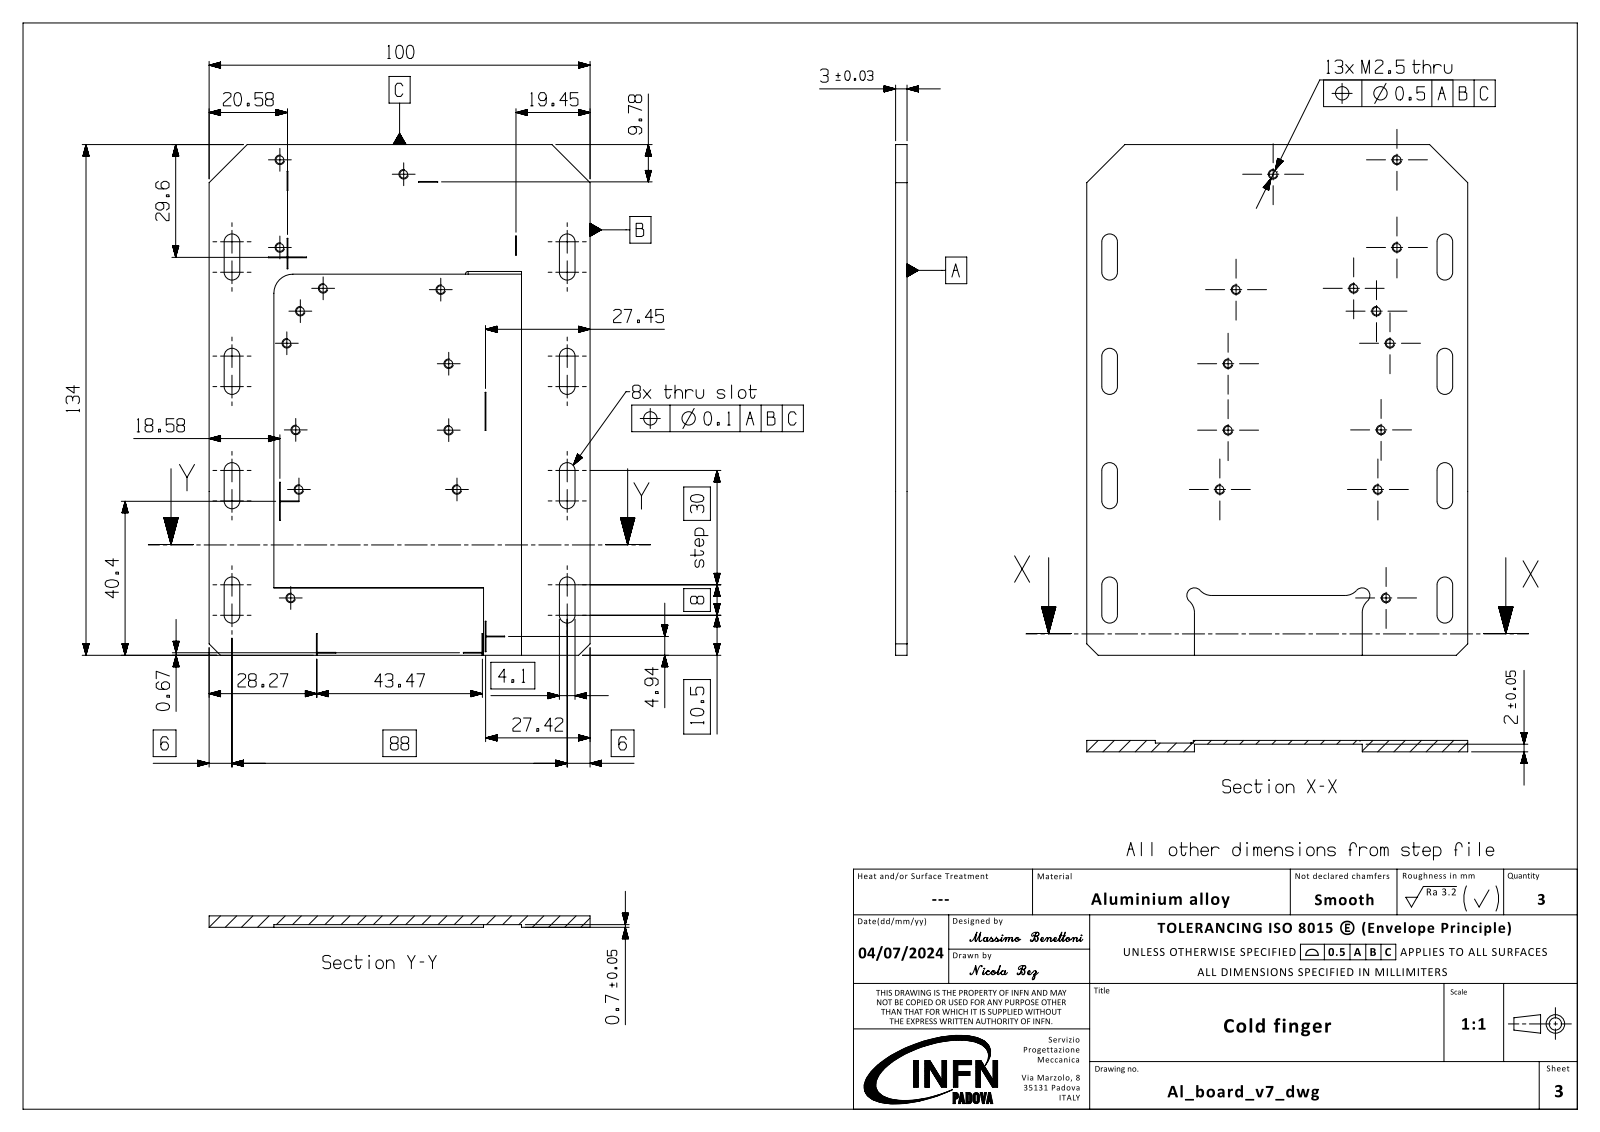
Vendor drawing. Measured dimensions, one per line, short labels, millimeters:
name: Al_board_assembly_v3_objects
written by: SIEMENS PLM Software NX2306.5001 (AUTOMOTIVE_DESIGN)
unit: mm
bodies: 1 solid, 142 faces (105 planar, 36 cylindrical, 1 other)
size: 134.02 × 100 × 4.29
volume: 33 512 mm³; area: 28 357 mm²
holes: 13× ⌀2.05
rounds: 16× R2.05, 4× R4, 2× R2, 1× R5
face distances: 3, 0.7, 2.3, 2, 1, 100, 134.01, 4.1, 3.95, 96.05
hole spacings: 8.47, 9.14, 15.61, 15.65, 15.72, 17.28, 17.43, 17.54
